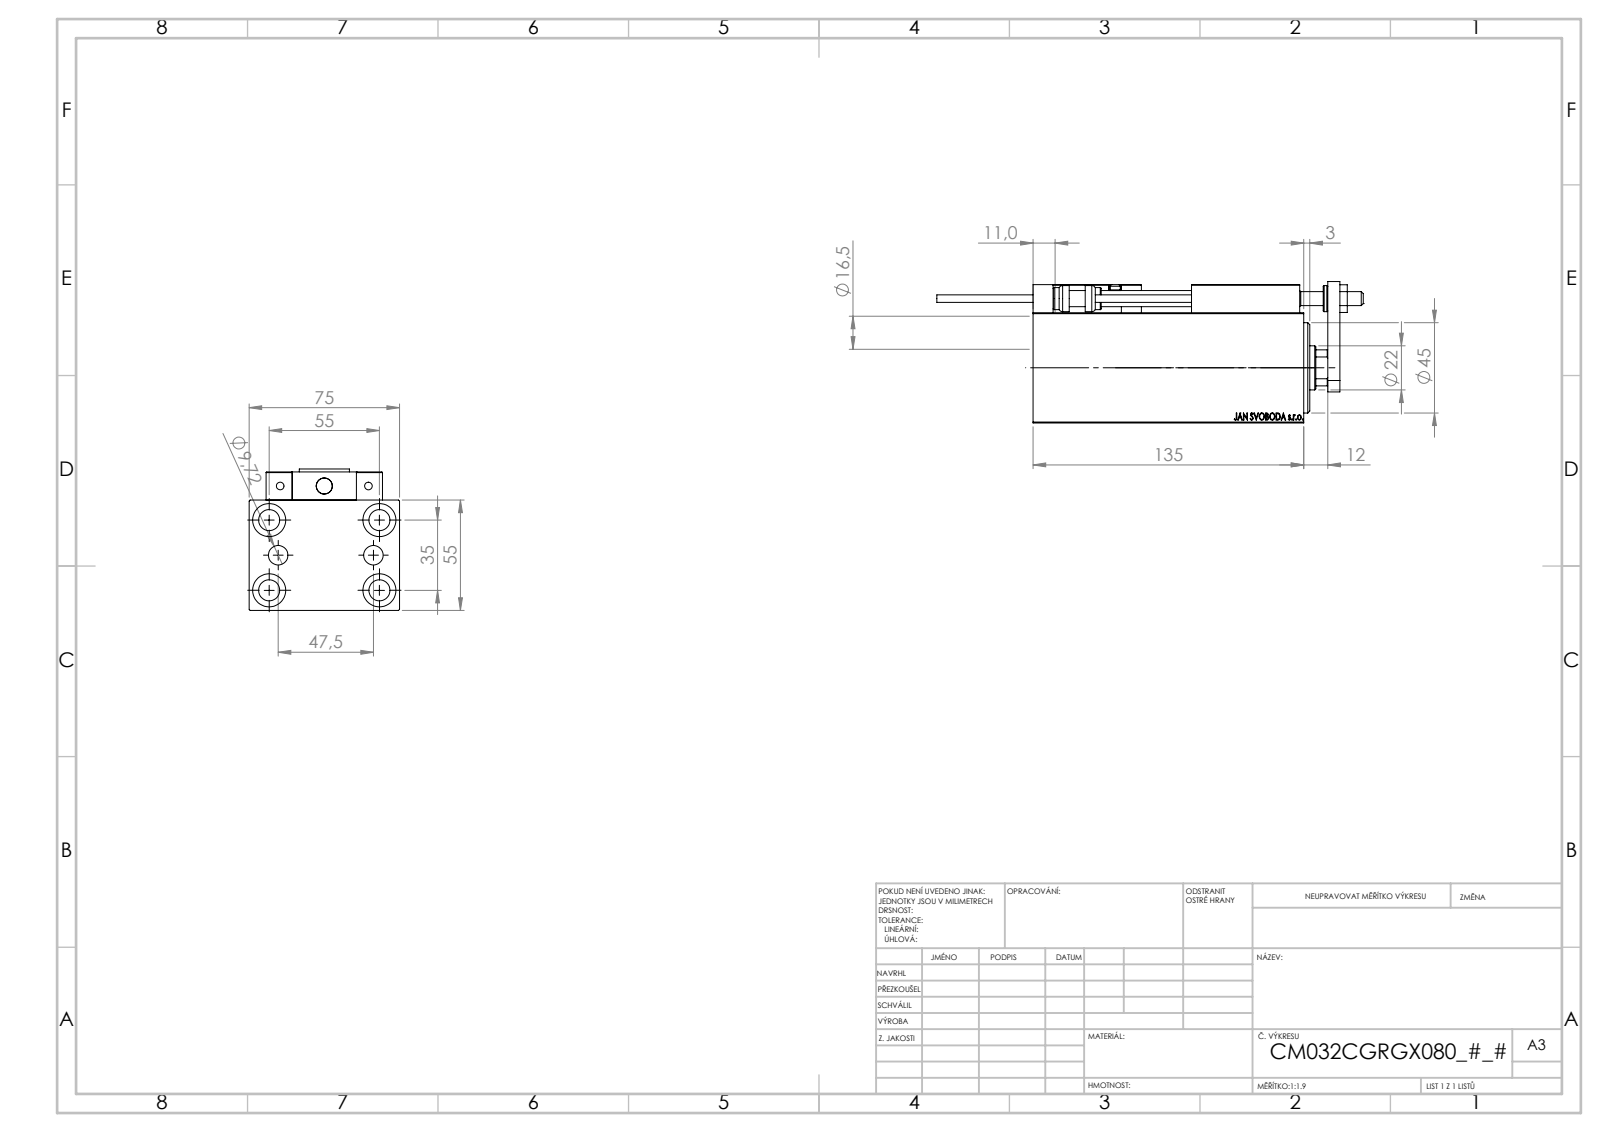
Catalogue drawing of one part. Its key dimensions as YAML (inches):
part_name: "ALLEN BOLT D8; V450CM_C_VCP; ZARAZKA; Block (+7 more)"
step_written_by: "SolidWorks 2019 (CONFIG_CONTROL_DESIGN)"
units: inches
bodies: {solids: 23, faces: 1278, planar: 560, cylindrical: 184, other: 534}
overall_size: [8.374, 2.953, 2.776]
volume: 31.53
surface_area: 192.1
round_holes:
  - {diameter: 0.157, count: 6}
  - {diameter: 0.315, count: 5}
  - {diameter: 0.413, count: 5}
  - {diameter: 0.65, count: 5}
  - {diameter: 0.126, count: 4}
  - {diameter: 0.197, count: 2}
  - {diameter: 0.383, count: 2}
  - {diameter: 0.276, count: 1}
  - {diameter: 0.866, count: 1}
  - {diameter: 1.004, count: 1}
  - {diameter: 1.26, count: 1}
  - {diameter: 1.339, count: 1}
round_bosses_or_shafts:
  - {diameter: 0.197, count: 2}
  - {diameter: 0.15, count: 2}
  - {diameter: 0.512, count: 1}
  - {diameter: 0.433, count: 1}
partial_cylinders:
  - {radius: 0.012, count: 30}
  - {radius: 0.118, count: 2}
  - {radius: 0.413, count: 1}
face_to_face_distances: [2.165, 2.953, 0.551, 0.394, 2.717, 0.984, 0.472, 0.197, 0.709, 0.118]
hole_center_spacings: [0.705, 1.283, 2.132, 0.448, 0.787, 0.935, 1.165, 1.169]
